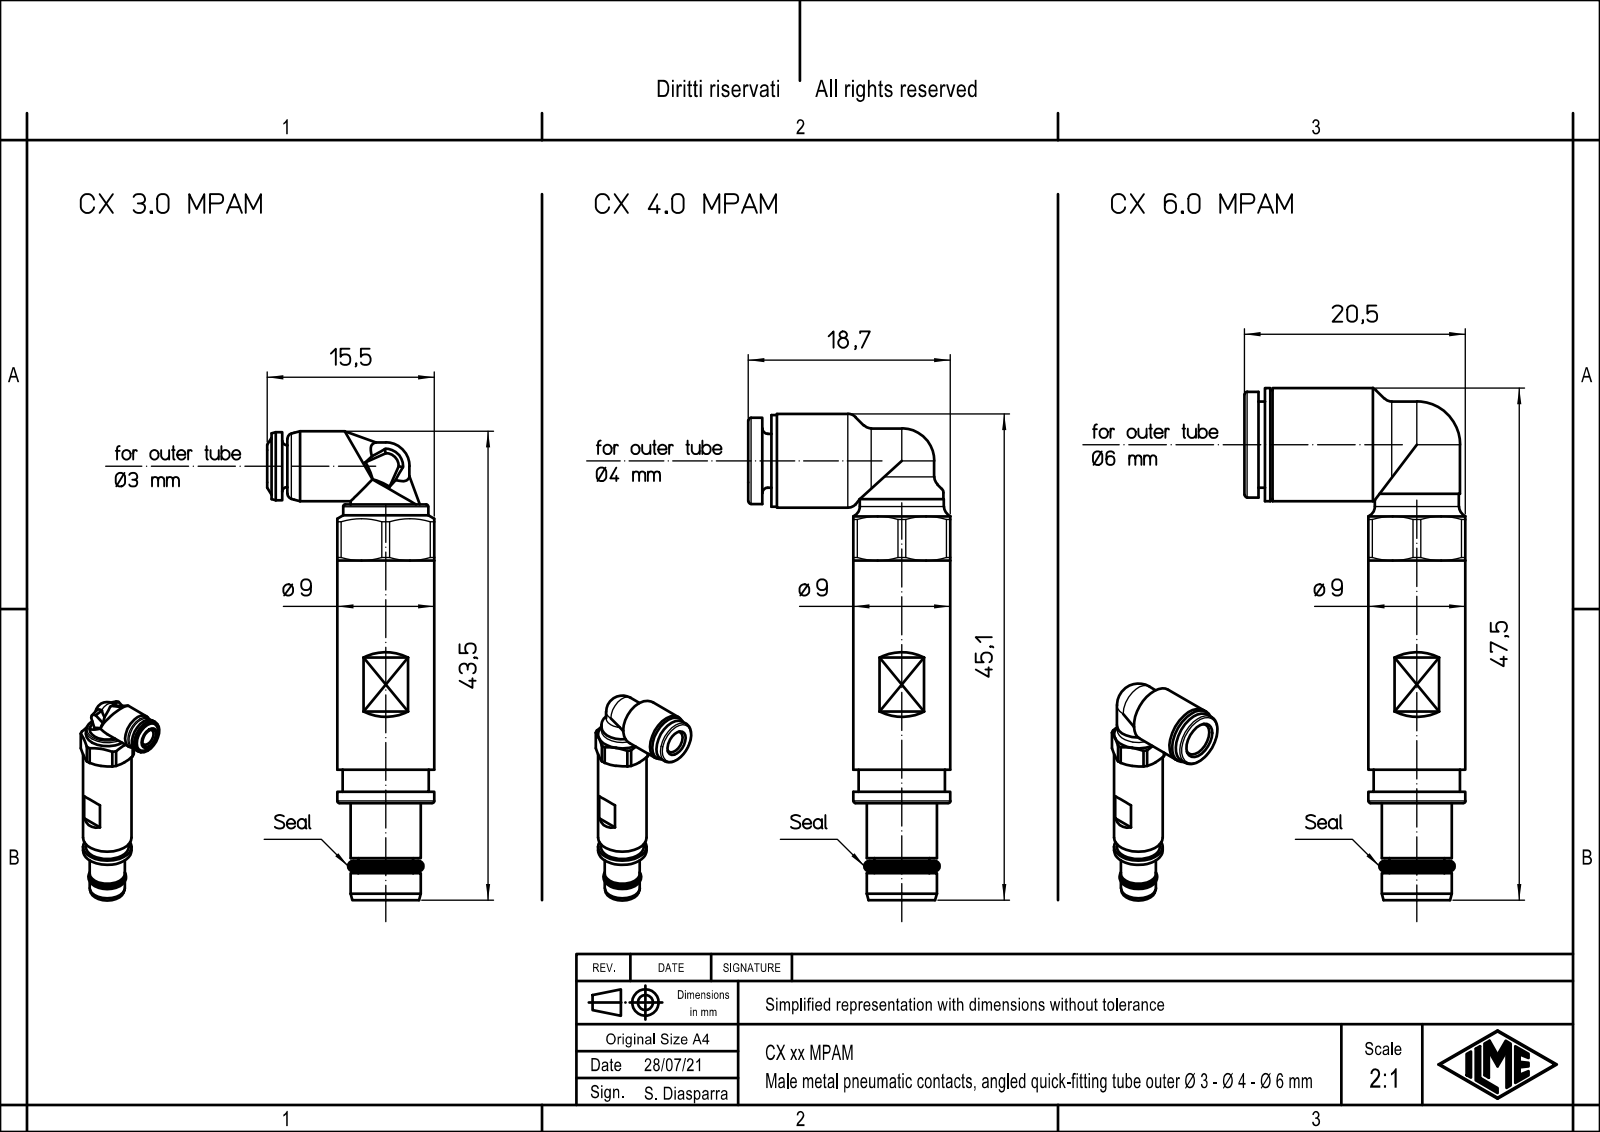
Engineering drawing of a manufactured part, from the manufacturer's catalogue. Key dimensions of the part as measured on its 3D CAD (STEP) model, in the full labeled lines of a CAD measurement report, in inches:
Part name (STEP PRODUCT): CX_4.0_MPAM
STEP written by: Creo Elements/Direct Modeling 20.1B 02-Apr-2019 (C) Parametric Technology GmbH (AUTOMOTIVE_DESIGN)
Units: inches
Bodies: 1 solid, 164 faces (55 planar, 49 cylindrical, 60 other)
Overall size (bounding box): 1.776 × 0.738 × 0.394
Volume: 0.136 in³ · Surface area: 3.562 in²
Round holes (diameter × count): ⌀0.118 ×2, ⌀0.15 ×1, ⌀0.165 ×1
Round bosses / shafts (diameter × count): ⌀0.315 ×2, ⌀0.354 ×1, ⌀0.343 ×1, ⌀0.335 ×1, ⌀0.307 ×1, ⌀0.303 ×1, ⌀0.256 ×1, ⌀0.201 ×1
Partial cylindrical surfaces — rounded edges, fillets, slot ends (radius × count): R0.118 ×2, R0.007 ×1, R0.008 ×1, R0.012 ×1, R0.013 ×1, R0.022 ×1, R0.022 ×1, R0.098 ×1
Main face-to-face distances: 0.354, 0.085, 0.051, 0.033, 0.315, 0.384, 0.333, 0.299, 0.738, 0.687
